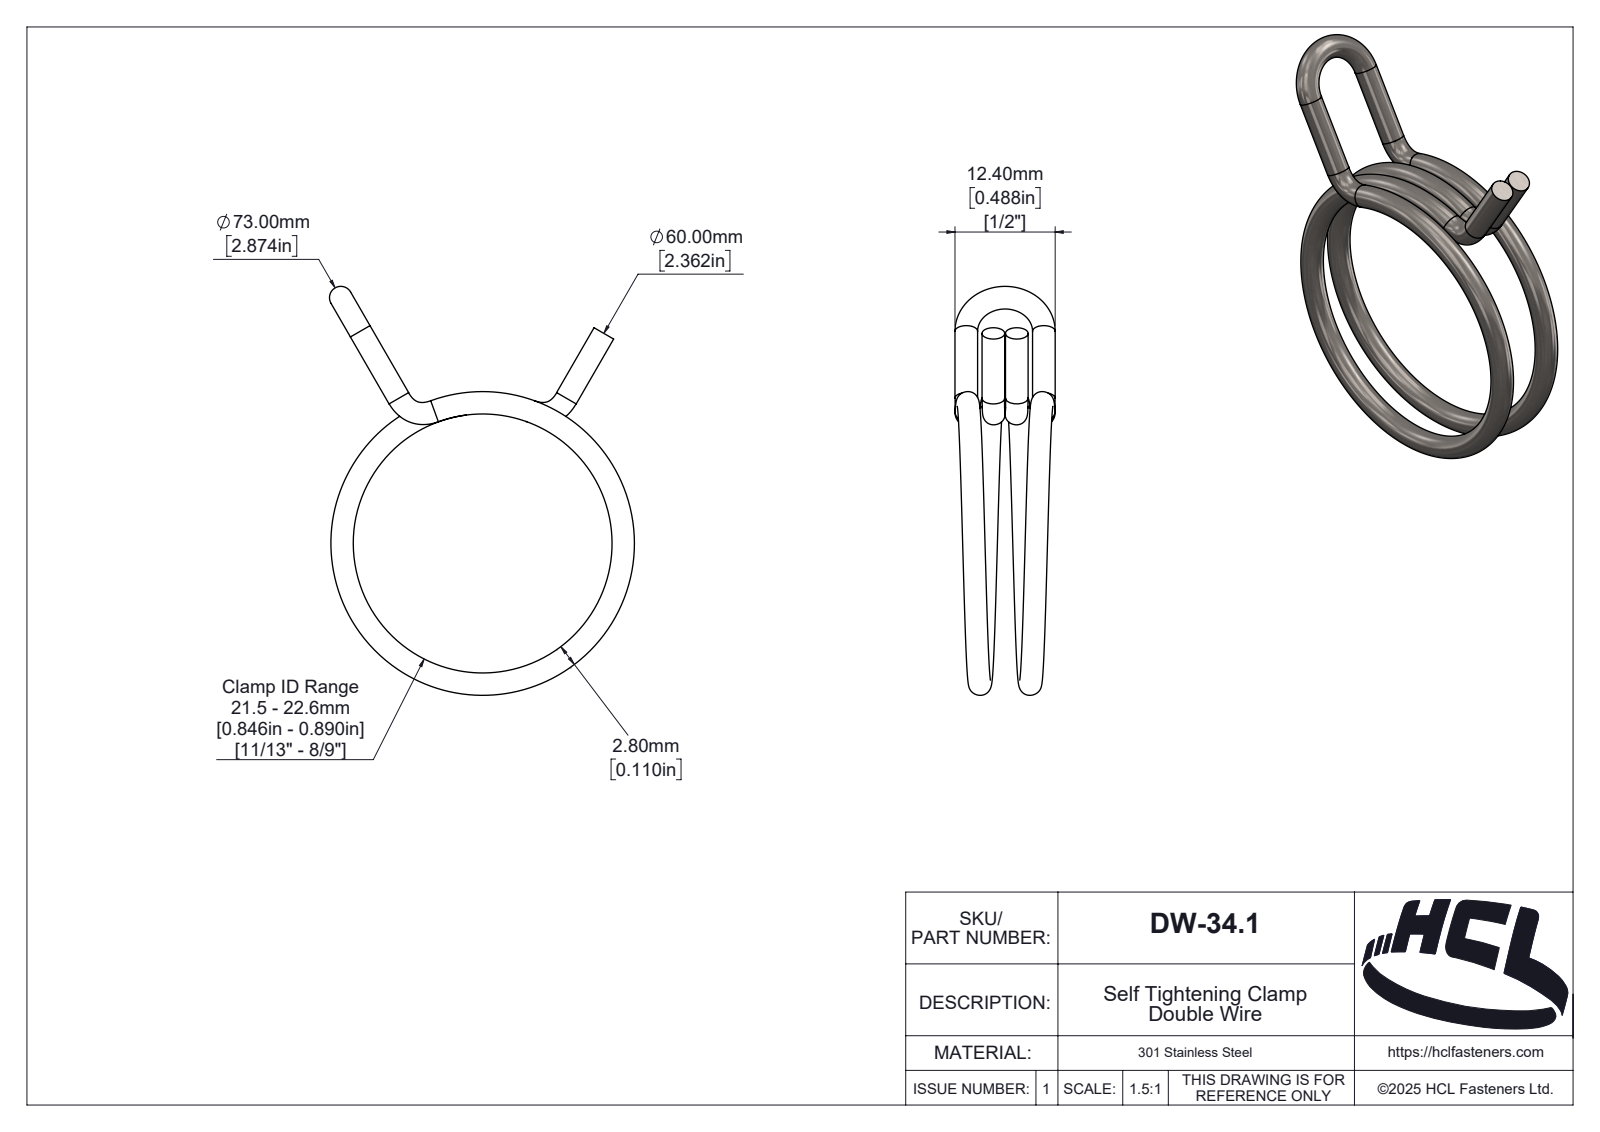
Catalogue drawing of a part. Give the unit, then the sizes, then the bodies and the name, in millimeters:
Units: millimetres
Overall size (bounding box): 50.58 × 37.73 × 12.4
Round bosses / shafts (diameter × count): ⌀2.8 ×4
Partial cylindrical surfaces — rounded edges, fillets, slot ends (radius × count): R0.16 ×1, R0.2 ×1, R0.21 ×1, R0.26 ×1, R0.36 ×1, R0.48 ×1, R0.6 ×1, R0.68 ×1
Volume: 1 923 mm³ · Surface area: 2 778 mm²
Bodies: 1 solid, 132 faces (14 planar, 53 cylindrical, 65 other)
Part name (STEP PRODUCT): DW-34.1
STEP written by: SolidWorks 2025 (AUTOMOTIVE_DESIGN)
